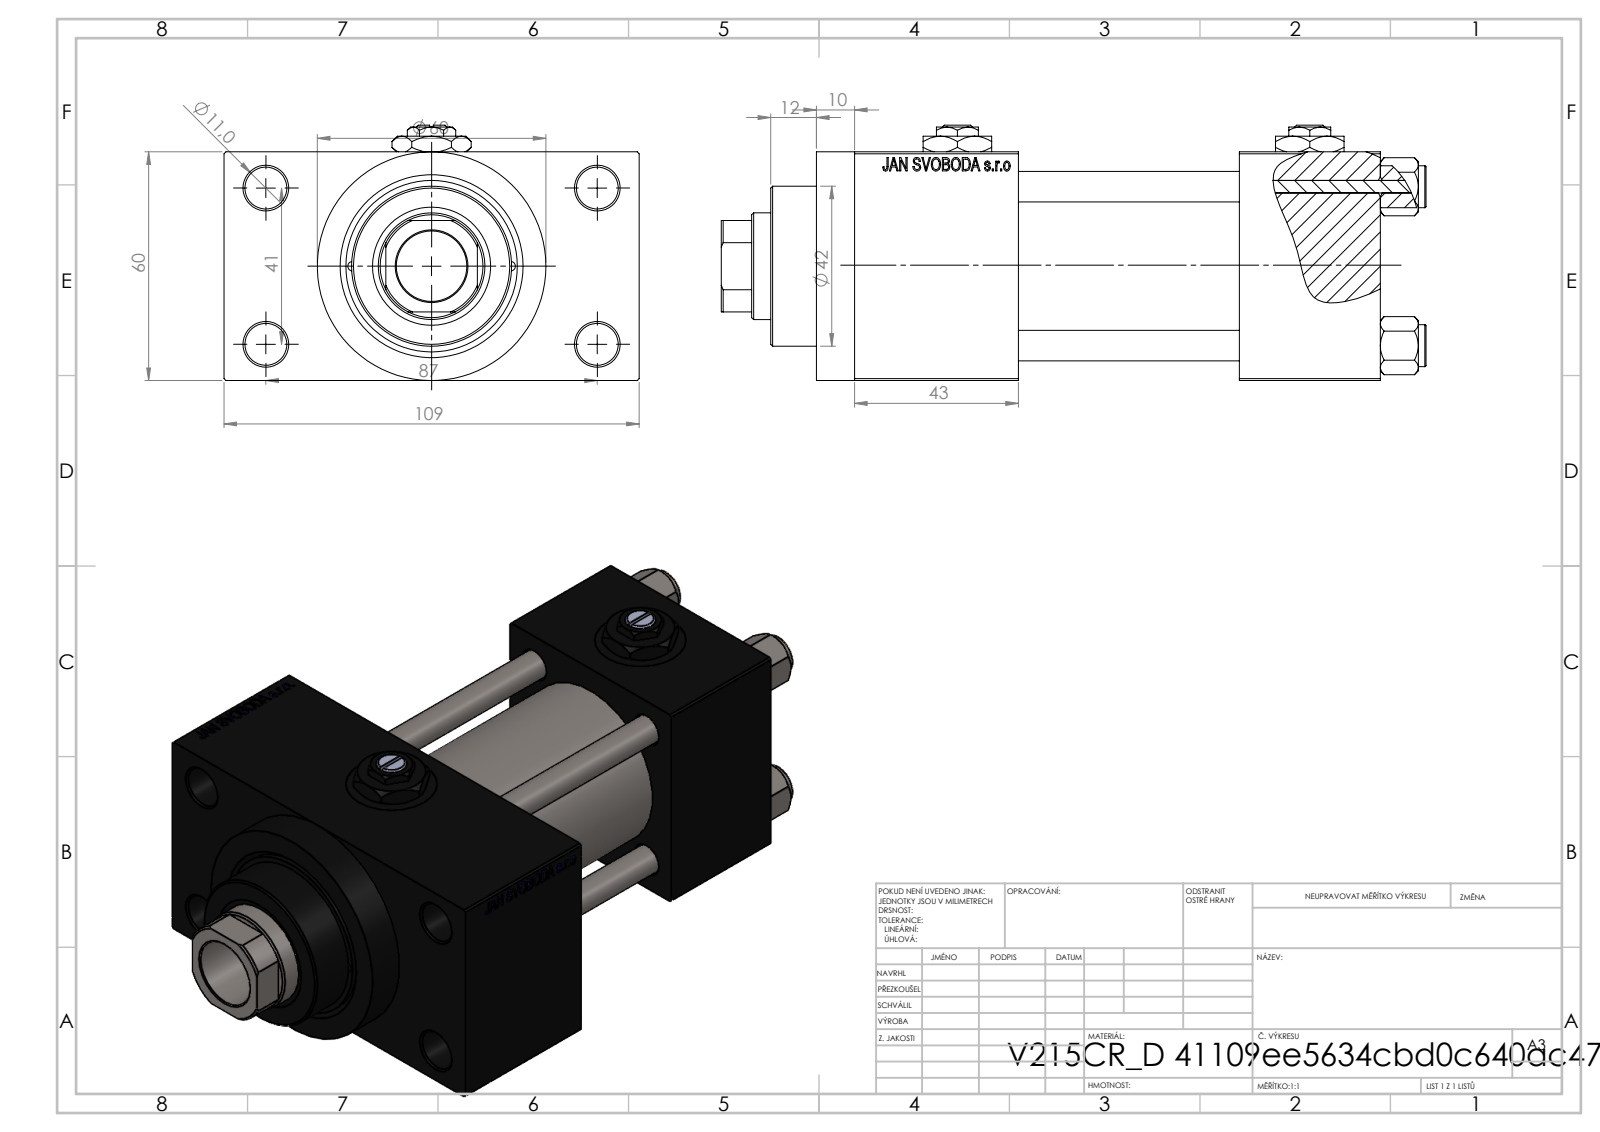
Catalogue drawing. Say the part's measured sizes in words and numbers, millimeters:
The part is named "V215CR_VCP_D; NUT_M5_D; Zatka_pro_OIL_PORT; V215_VC_A (+2 more)". Its 3-D file was written by "SolidWorks 2019 (CONFIG_CONTROL_DESIGN)". It is 13 solids with 1215 faces: 550 planar, 103 cylindrical and 562 other. Overall it measures 185 by 109 by 67 millimeters. Its volume is 526 480 cubic millimeters and its surface area 131 721 square millimeters. Round holes: 4 of diameter 8, 4 of diameter 11, 4 of diameter 16.66, 4 of diameter 24, 3 of diameter 7, 2 of diameter 2.5, 1 of diameter 18.5, 1 of diameter 28, 1 of diameter 31, 1 of diameter 40, 1 of diameter 45. Round bosses or shafts: 4 of diameter 11, 1 of diameter 60, 1 of diameter 46, 1 of diameter 42. Partial cylindrical surfaces (rounded edges, fillets, slot ends): 1 of radius 13.5. The main face-to-face distances are 60, 58, 24.5, 84.5, 37, 95, 138, 101, 43, 109. The hole center spacings are 20.85, 22.65, 29.49, 30.62, 41.7, 46.53, 47.15, 48.09.
